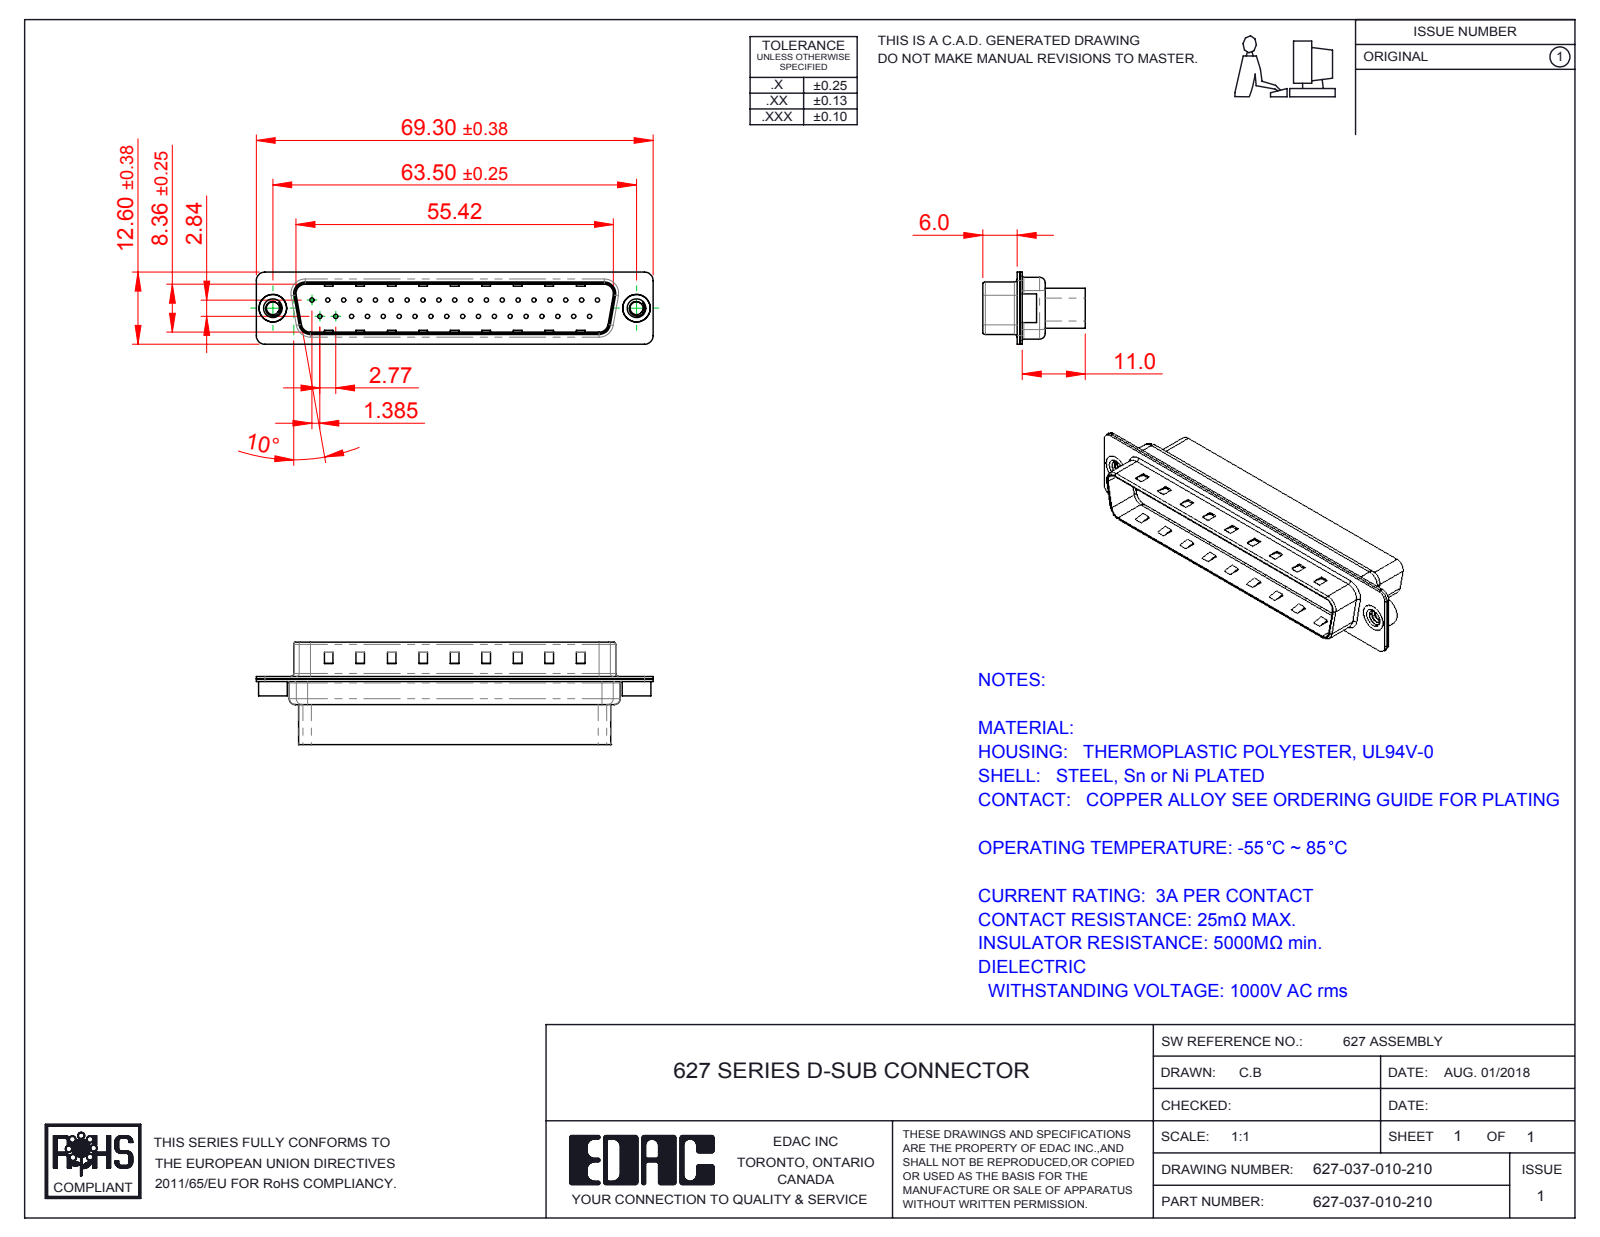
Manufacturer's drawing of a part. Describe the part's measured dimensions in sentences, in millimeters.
The part is named "627 Shell Front_37 Contacts; 627 Housing_37 HP; 627 4-40 Threaded Rivet; 627 Shell Rear_37 Contacts (+1 more)". Its 3-D file was written by "SolidWorks 2016 (CONFIG_CONTROL_DESIGN)". It is 5 solids with 704 faces: 277 planar, 361 cylindrical and 66 other. Overall it measures 69.3 by 17.9 by 12.6 millimeters. Its volume is 5 019 cubic millimeters and its surface area 9 026 square millimeters. Round holes: 37 of diameter 0.75, 37 of diameter 1.6, 37 of diameter 2, 2 of diameter 2.26, 2 of diameter 4, 2 of diameter 4.8. Round bosses or shafts: 2 of diameter 5, 2 of diameter 4.9. Partial cylindrical surfaces (rounded edges, fillets, slot ends): 16 of radius 1.5, 12 of radius 2, 8 of radius 0.5, 8 of radius 1.6, 4 of radius 0.25, 4 of radius 0.6, 4 of radius 0.65, 4 of radius 0.9. The main face-to-face distances are 0.4, 0.82, 9.58, 0.68, 7.68, 0.45, 1.08, 8.08, 8.76, 7. The hole center spacings are 3.16, 2.77, 5.54, 8.31, 5.04, 10.1, 11.08, 12.78.
